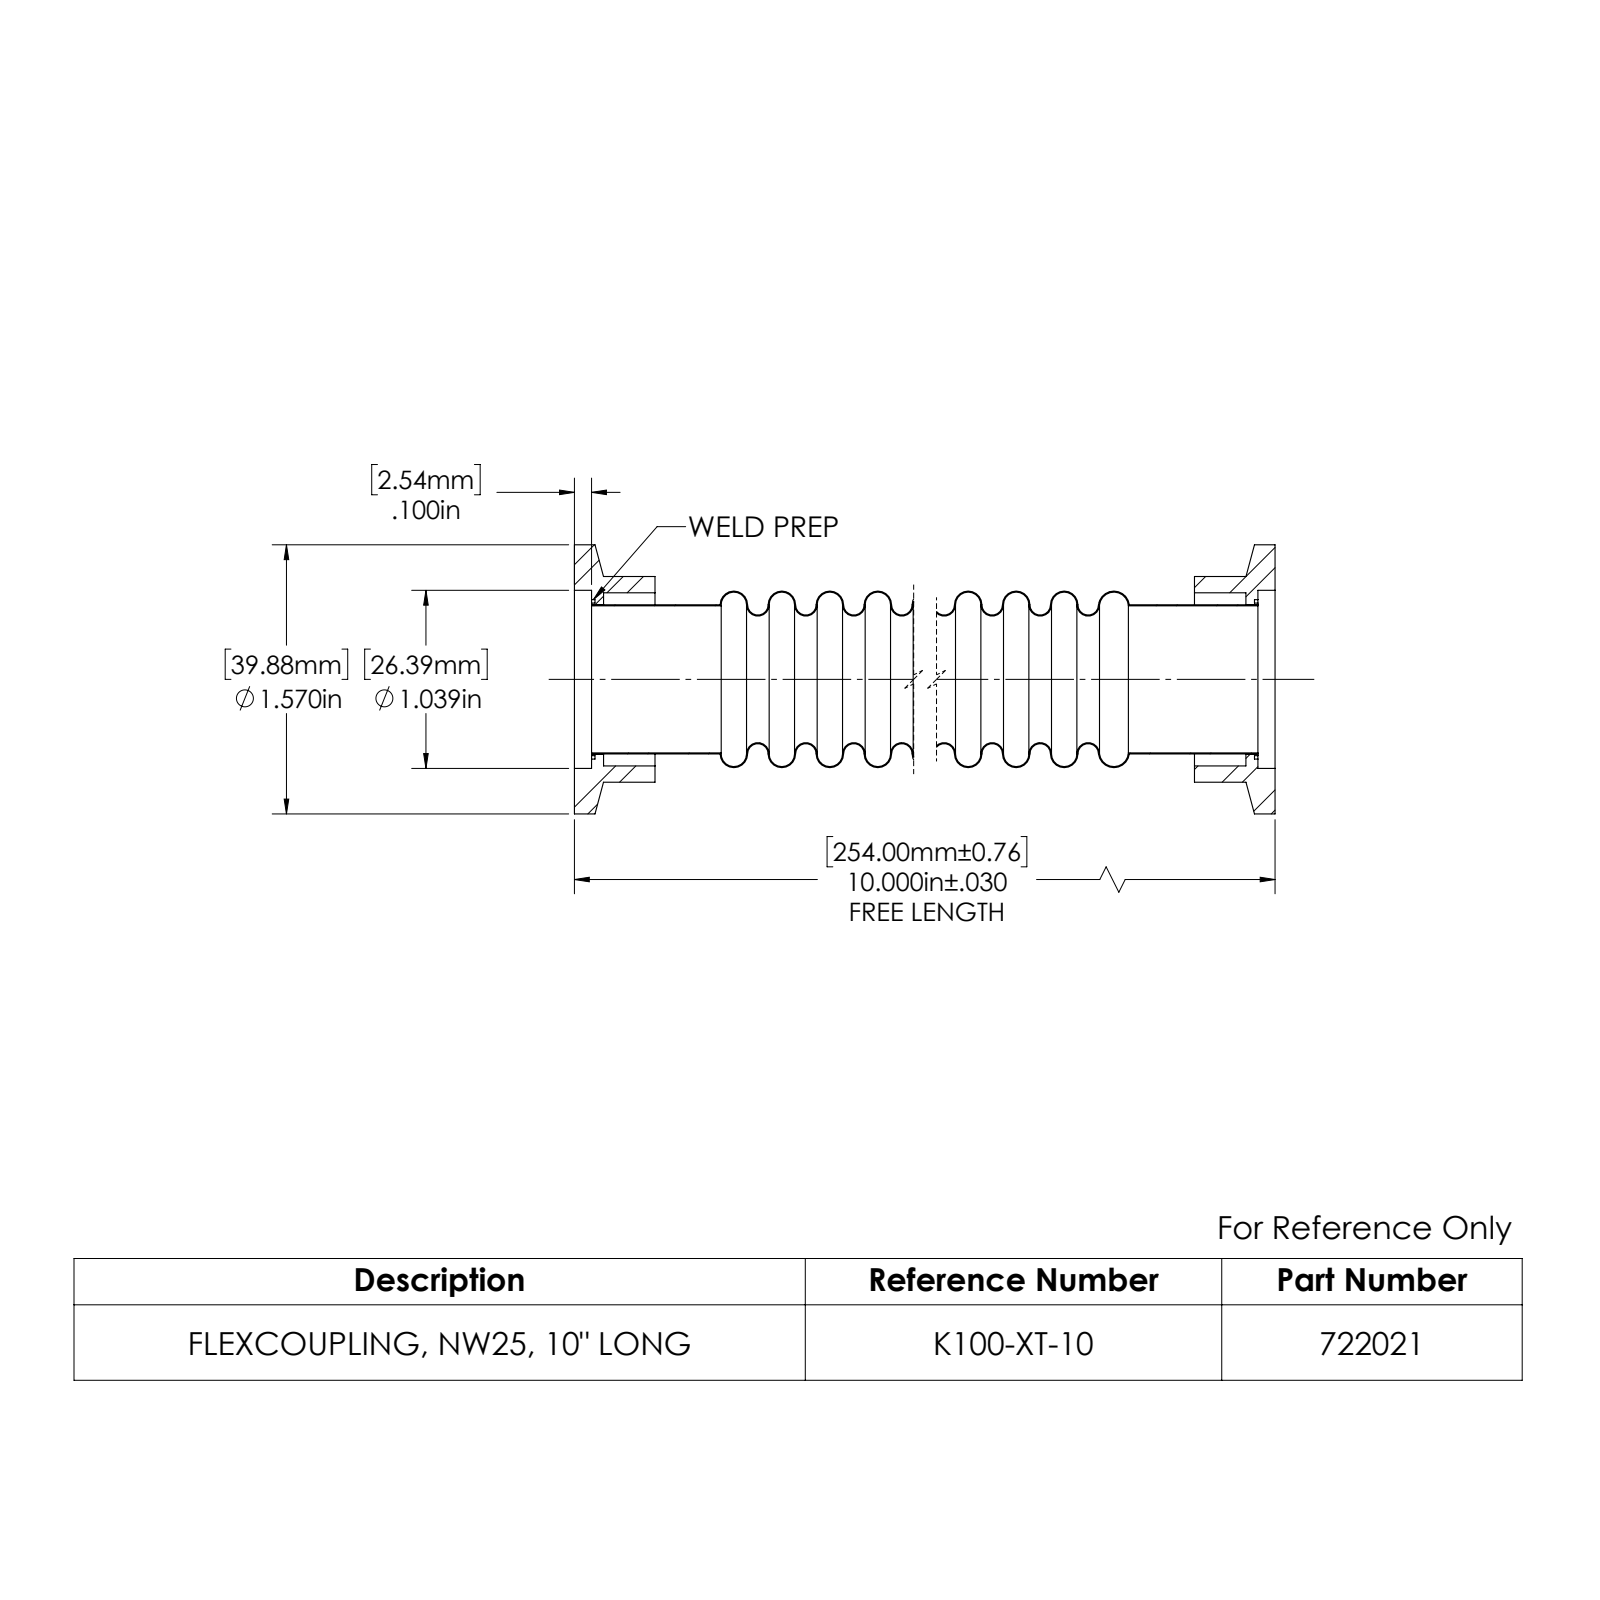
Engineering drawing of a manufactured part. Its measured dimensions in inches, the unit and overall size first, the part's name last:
Units: inches
Overall size (bounding box): 10 × 1.57 × 1.57
Round holes (diameter × count): ⌀0.858 ×1, ⌀0.87 ×1, ⌀1.01 ×1, ⌀1.039 ×1
Round bosses / shafts (diameter × count): ⌀1.57 ×1, ⌀1.2 ×1
Main face-to-face distances: 10, 0.47, 9.53, 0.1, 9.9, 0.37, 9.43, 0.17, 9.83, 0.07
Volume: 0.804 in³ · Surface area: 92.75 in²
Bodies: 3 solids, 394 faces (10 planar, 28 cylindrical, 356 other)
Part name (STEP PRODUCT): 713002; 722021
STEP written by: SolidWorks 2022 (AUTOMOTIVE_DESIGN)
